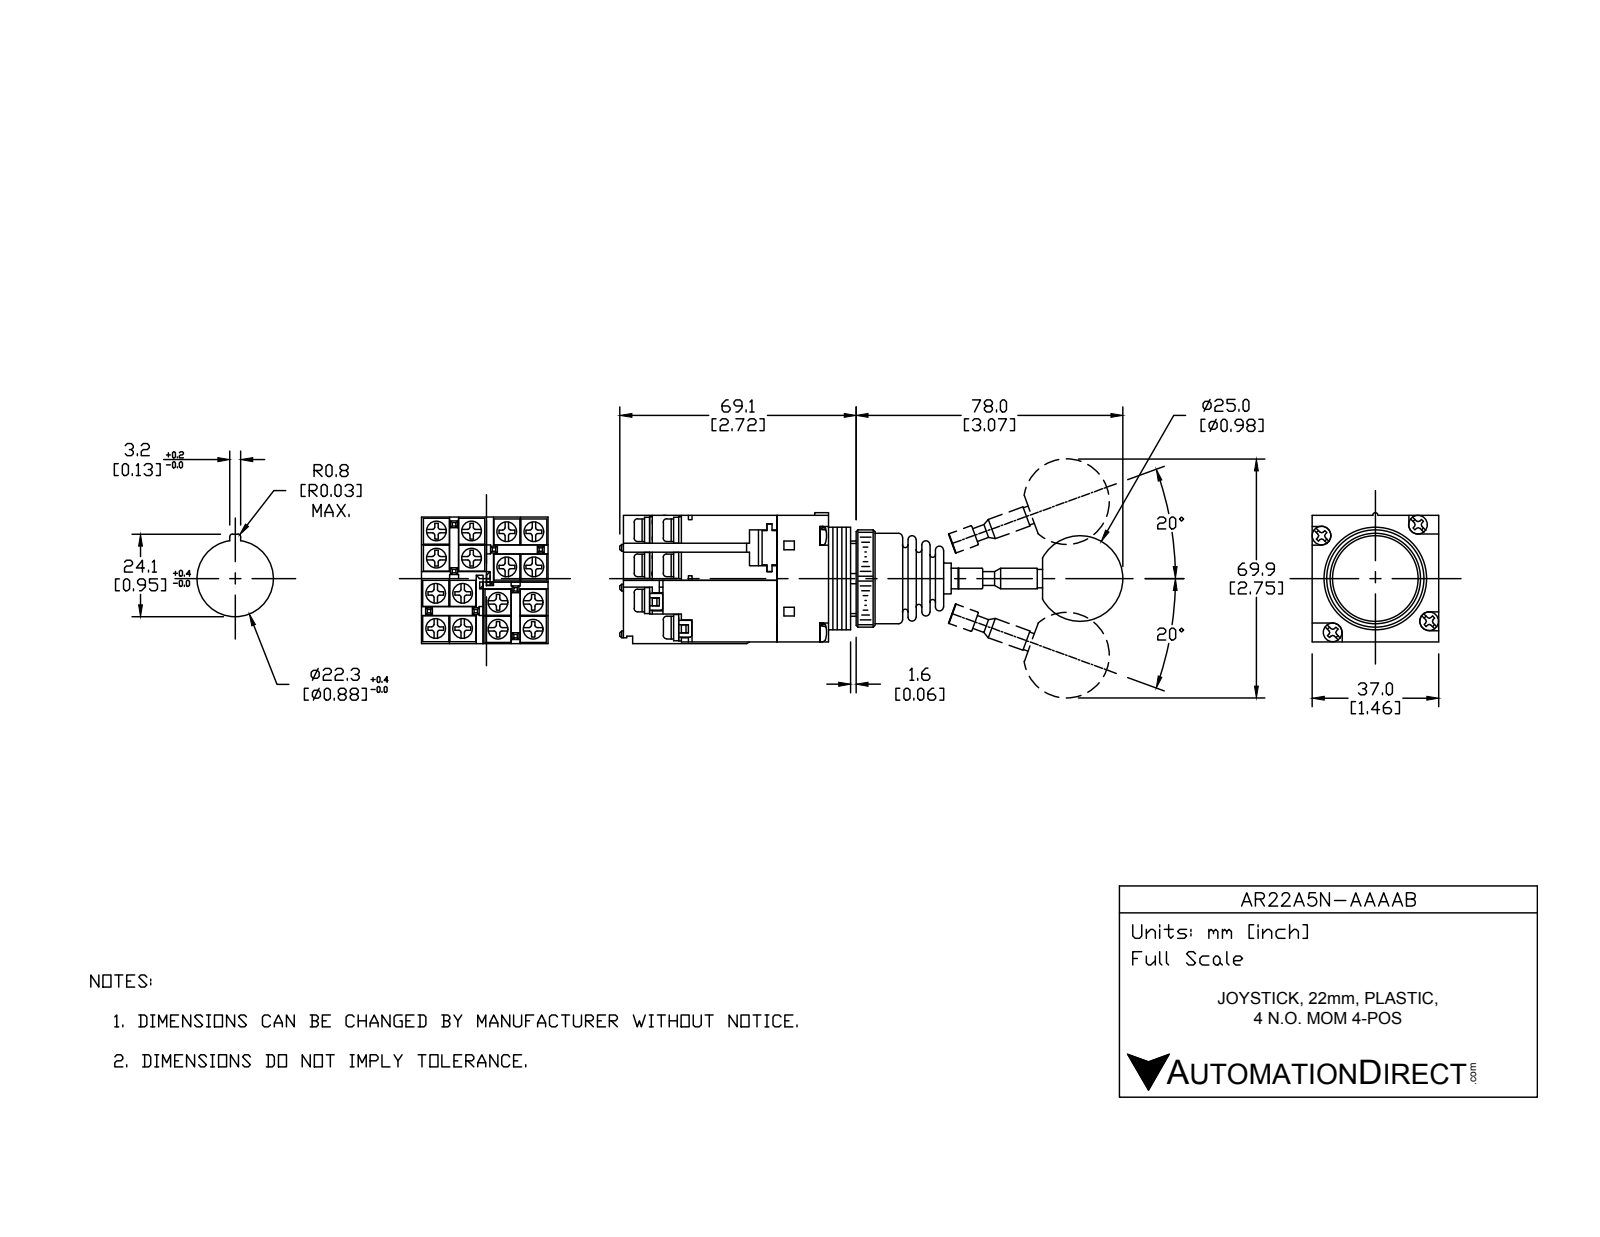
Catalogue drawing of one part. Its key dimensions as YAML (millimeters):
part_name: "AR22A5N-AAAAB"
step_written_by: "SolidWorks 2017 (AUTOMOTIVE_DESIGN)"
units: millimeters
bodies: {solids: 26, faces: 439, planar: 285, cylindrical: 64, other: 90}
overall_size: [146.1, 37, 37]
volume: 85637
surface_area: 38413
round_holes:
  - {diameter: 6.2, count: 1}
  - {diameter: 16, count: 1}
  - {diameter: 22.5, count: 1}
  - {diameter: 26, count: 1}
round_bosses_or_shafts:
  - {diameter: 5.8, count: 8}
  - {diameter: 4, count: 4}
  - {diameter: 30, count: 1}
  - {diameter: 28, count: 1}
  - {diameter: 22, count: 1}
  - {diameter: 6, count: 1}
partial_cylinders:
  - {radius: 2.8, count: 2}
  - {radius: 3, count: 2}
face_to_face_distances: [18.75, 18.25, 37, 0.5, 1.3, 2.6, 3.9, 15, 10.35, 7.9]
